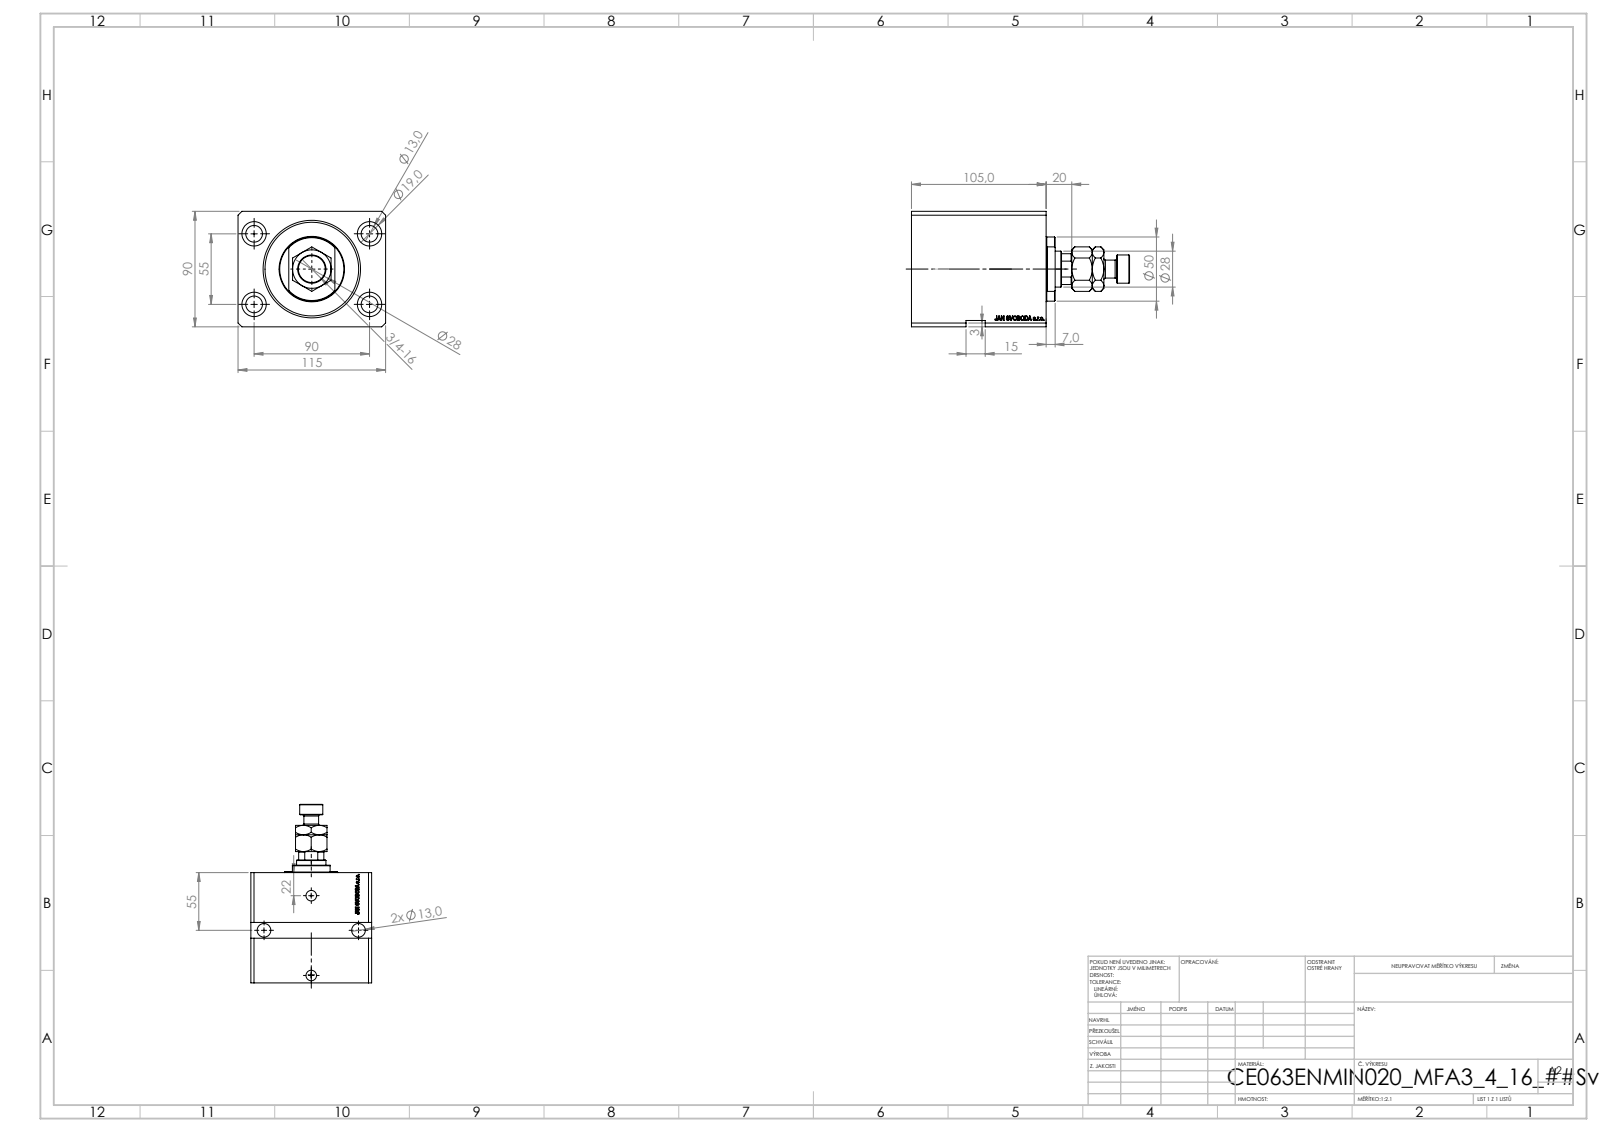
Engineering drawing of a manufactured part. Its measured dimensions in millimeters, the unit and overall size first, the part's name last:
Units: millimetres
Overall size (bounding box): 170 × 115 × 90
Round holes (diameter × count): ⌀13 ×6, ⌀1.25 ×4, ⌀19 ×4, ⌀10 ×2, ⌀13.16 ×2, ⌀20 ×2, ⌀18.5 ×1, ⌀28 ×1, ⌀63 ×1, ⌀76 ×1
Round bosses / shafts (diameter × count): ⌀50 ×1, ⌀22 ×1, ⌀14 ×1
Partial cylindrical surfaces — rounded edges, fillets, slot ends (radius × count): R13.5 ×1
Main face-to-face distances: 20, 90, 115, 85, 105, 17.9, 87.1, 67.1, 40, 65
Hole centre spacings: 52.74, 55, 90, 55.8, 61.88, 62.24, 105.48, 0.53
Volume: 967 609 mm³ · Surface area: 149 790 mm²
Bodies: 4 solids, 989 faces (483 planar, 88 cylindrical, 418 other)
Part name (STEP PRODUCT): V250CE_E_Body; V250CE_VC_E; MFA; V250CE_C_VCP
STEP written by: SolidWorks 2019 (CONFIG_CONTROL_DESIGN)
